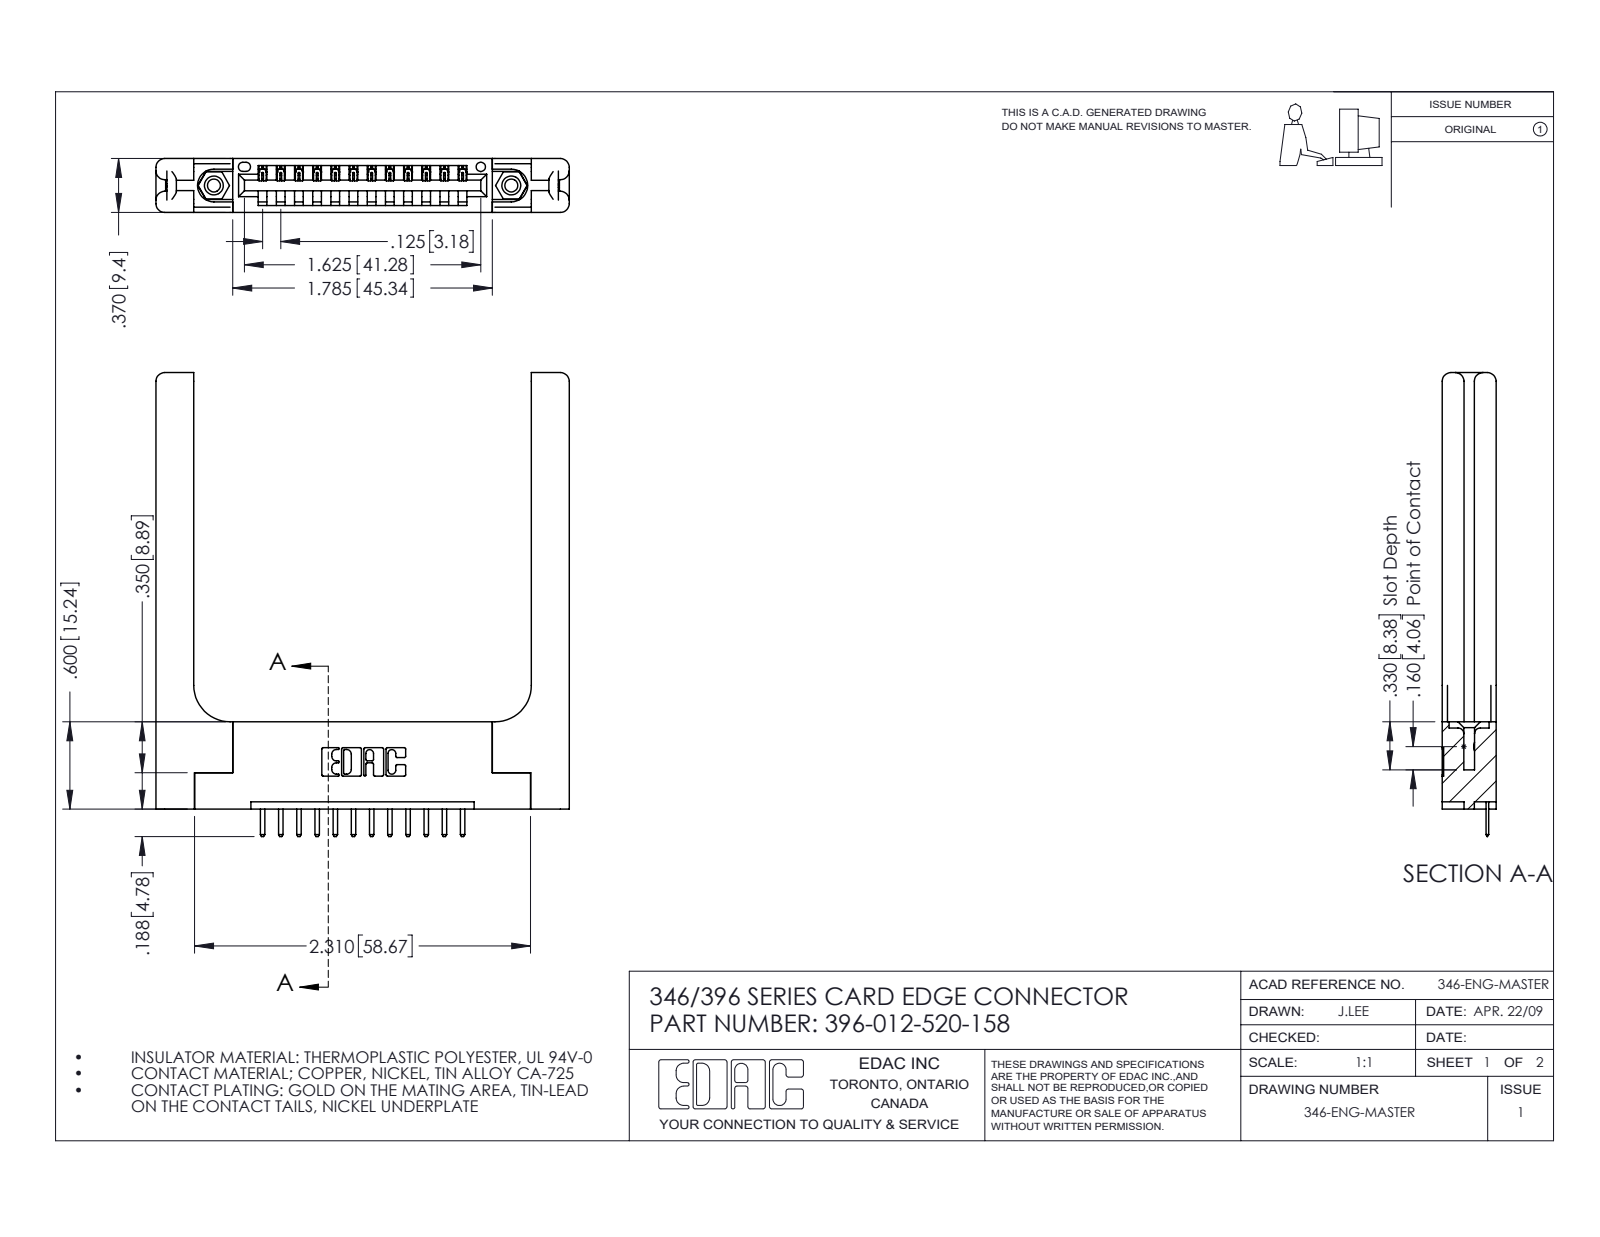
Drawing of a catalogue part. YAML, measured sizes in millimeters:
part_name: "346-220-058_345-220-058; 345-250-001_345-250-001-102; 396-012-520-158; 345-292-001_345-293-120 (+1 more)"
step_written_by: "SolidWorks 2016 (CONFIG_CONTROL_DESIGN)"
units: millimeters
bodies: {solids: 17, faces: 1122, planar: 728, cylindrical: 334, other: 60}
overall_size: [81, 72.2, 9.4]
volume: 14200
surface_area: 13060
round_holes:
  - {diameter: 2.3, count: 2}
  - {diameter: 3.2, count: 2}
  - {diameter: 4, count: 2}
  - {diameter: 1.6, count: 1}
round_bosses_or_shafts:
  - {diameter: 3.9, count: 2}
partial_cylinders:
  - {radius: 0.3, count: 26}
  - {radius: 0.2, count: 24}
  - {radius: 0.3, count: 22}
  - {radius: 1.5, count: 16}
  - {radius: 0.2, count: 6}
  - {radius: 0.8, count: 6}
  - {radius: 0.7, count: 3}
  - {radius: 0.8, count: 2}
face_to_face_distances: [9.4, 3.8, 1.8, 3.8, 5.6, 1.2, 8.2, 2.6, 4.4, 6.4]
hole_center_spacings: [6.2, 46.7, 51.9]
